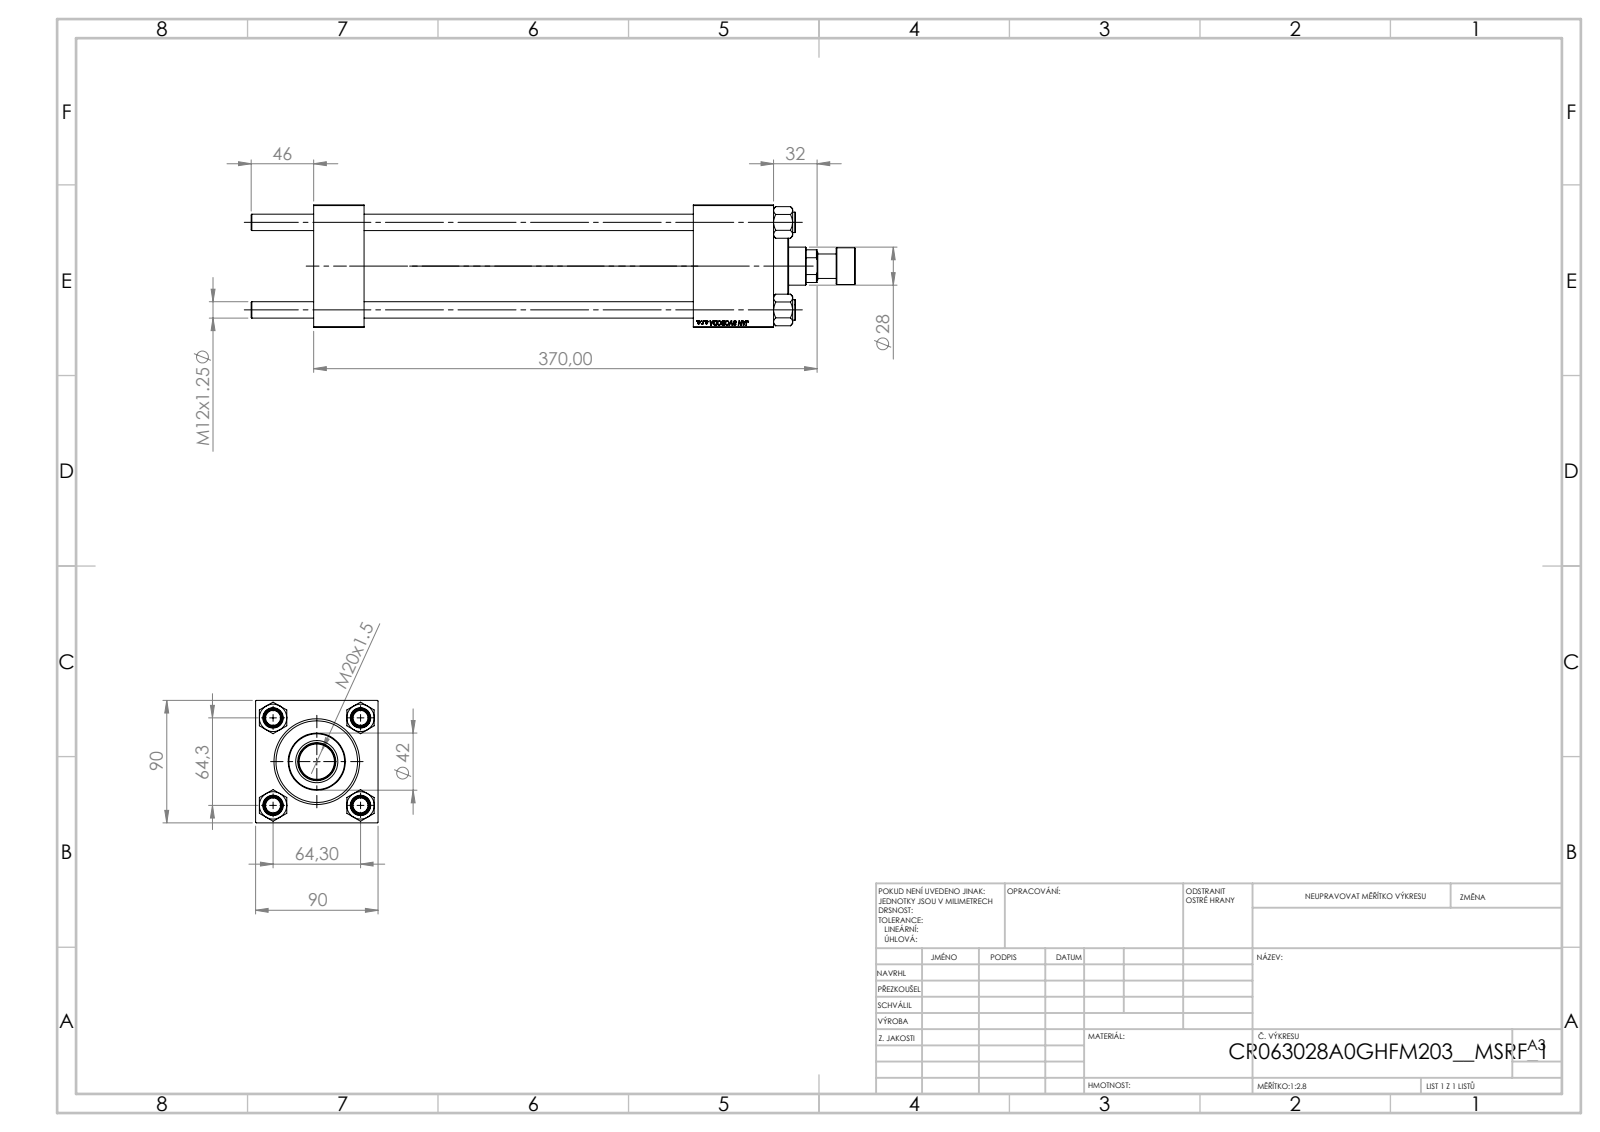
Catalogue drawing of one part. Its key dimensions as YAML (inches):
part_name: "V215CR_BODY_A; V215_VC_A; V215CR_ROD_END_F; CR025_012_A_0_G_A_G_M_020_+#_##_TYCINKA (+2 more)"
step_written_by: "SolidWorks 2019 (CONFIG_CONTROL_DESIGN)"
units: inches
bodies: {solids: 12, faces: 1148, planar: 524, cylindrical: 82, other: 542}
overall_size: [17.48, 3.543, 3.543]
volume: 79.45
surface_area: 493.1
round_holes:
  - {diameter: 0.472, count: 4}
  - {diameter: 0.276, count: 2}
  - {diameter: 0.825, count: 2}
  - {diameter: 1.181, count: 2}
  - {diameter: 0.728, count: 1}
  - {diameter: 1.102, count: 1}
  - {diameter: 1.22, count: 1}
  - {diameter: 1.969, count: 1}
  - {diameter: 2.362, count: 1}
  - {diameter: 2.48, count: 1}
round_bosses_or_shafts:
  - {diameter: 0.591, count: 4}
  - {diameter: 2.717, count: 1}
  - {diameter: 1.654, count: 1}
  - {diameter: 1.063, count: 1}
  - {diameter: 0.709, count: 1}
face_to_face_distances: [3.543, 1.457, 13.307, 11.85, 10.984, 9.528, 2.323, 12.177, 10.72, 1.193]
hole_center_spacings: [1.79, 2.531, 3.58, 11.043]
